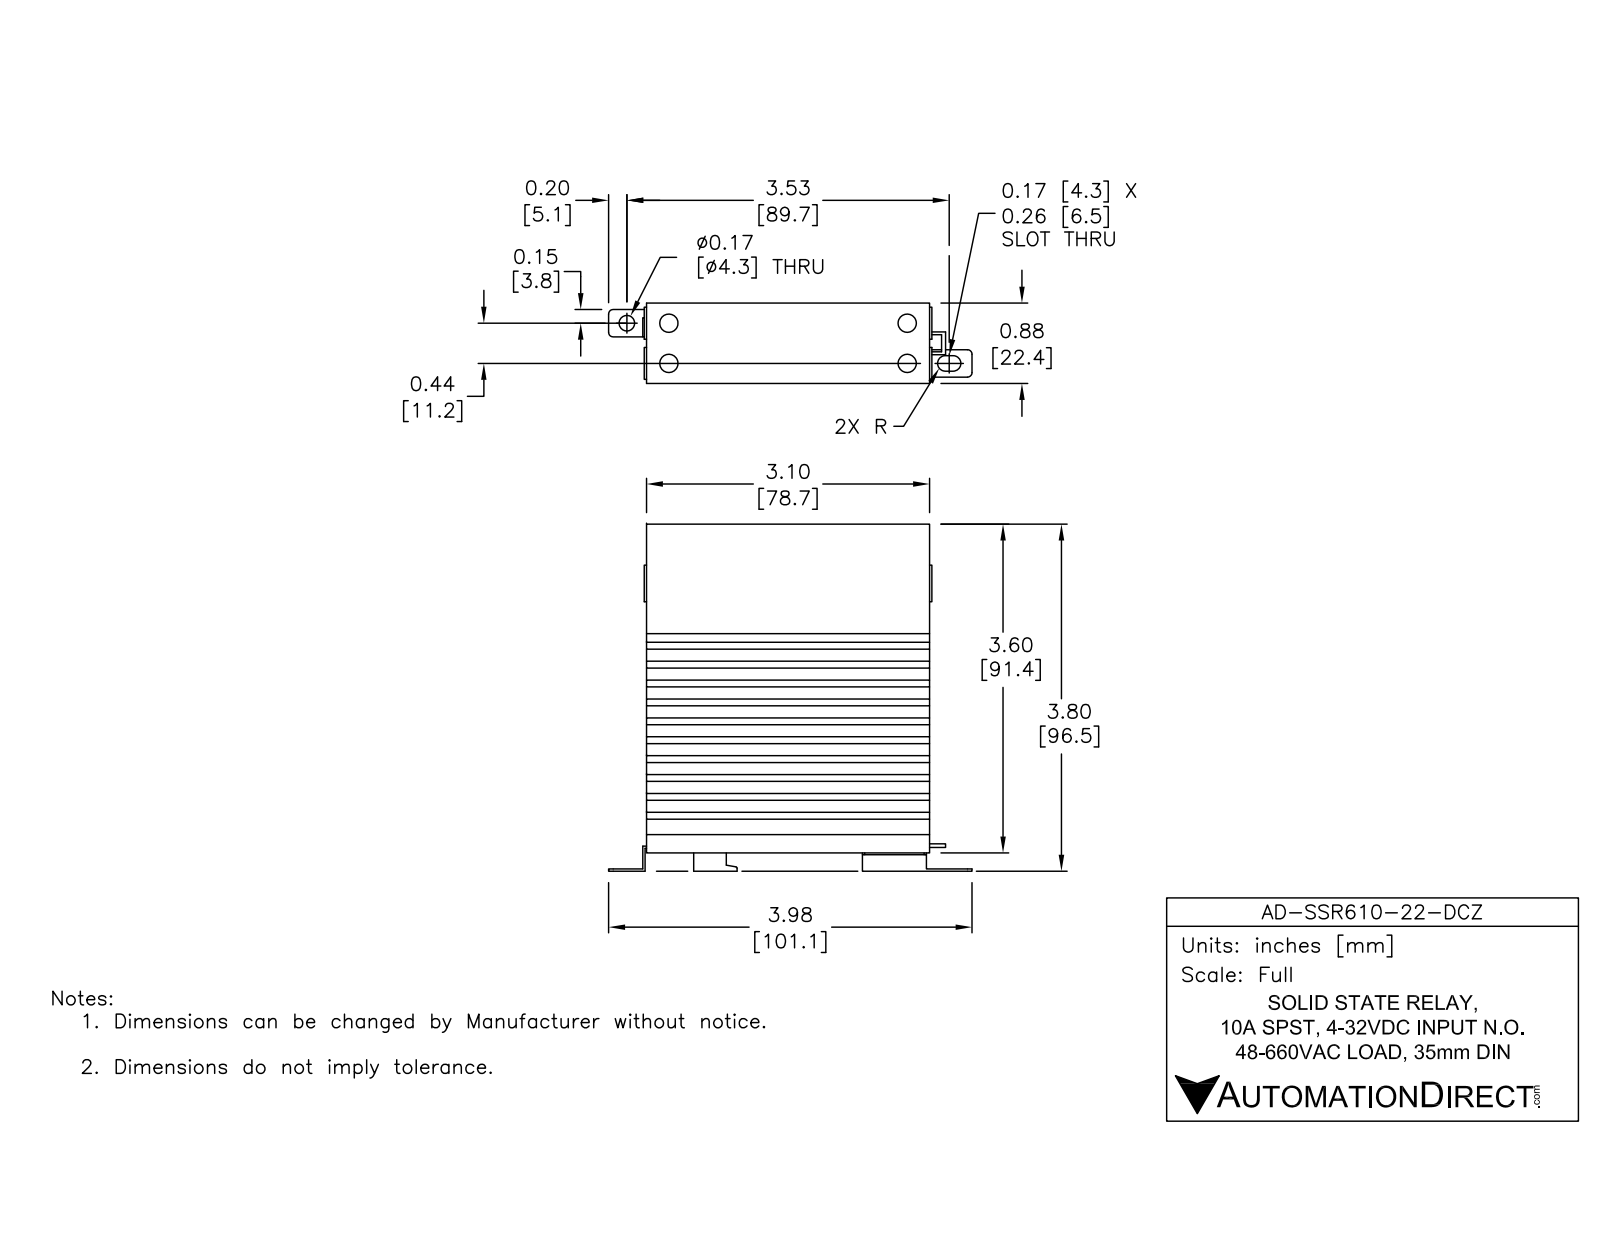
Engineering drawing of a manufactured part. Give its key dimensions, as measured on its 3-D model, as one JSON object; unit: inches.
{"part_name": "AD-SSR610-22-DCZ", "step_written_by": "SolidWorks 2014 (AUTOMOTIVE_DESIGN)", "units": "inches", "bodies": {"solids": 1, "faces": 215, "planar": 195, "cylindrical": 20, "other": 0}, "overall_size": [3.98, 3.8, 0.88], "volume_in3": 7.136, "surface_area_in2": 74.91, "round_holes": [[0.2, 4], [0.17, 1]], "partial_cylinders_radius": [[0.05, 6], [0.085, 2], [0.015, 1]], "face_to_face_distances": [0.62, 0.207, 0.827, 0.414, 0.132, 0.489, 0.339, 0.413, 0.075, 0.207], "hole_center_spacings": [0.44, 2.61, 2.647, 0.46, 0.637, 3.07, 3.102]}
